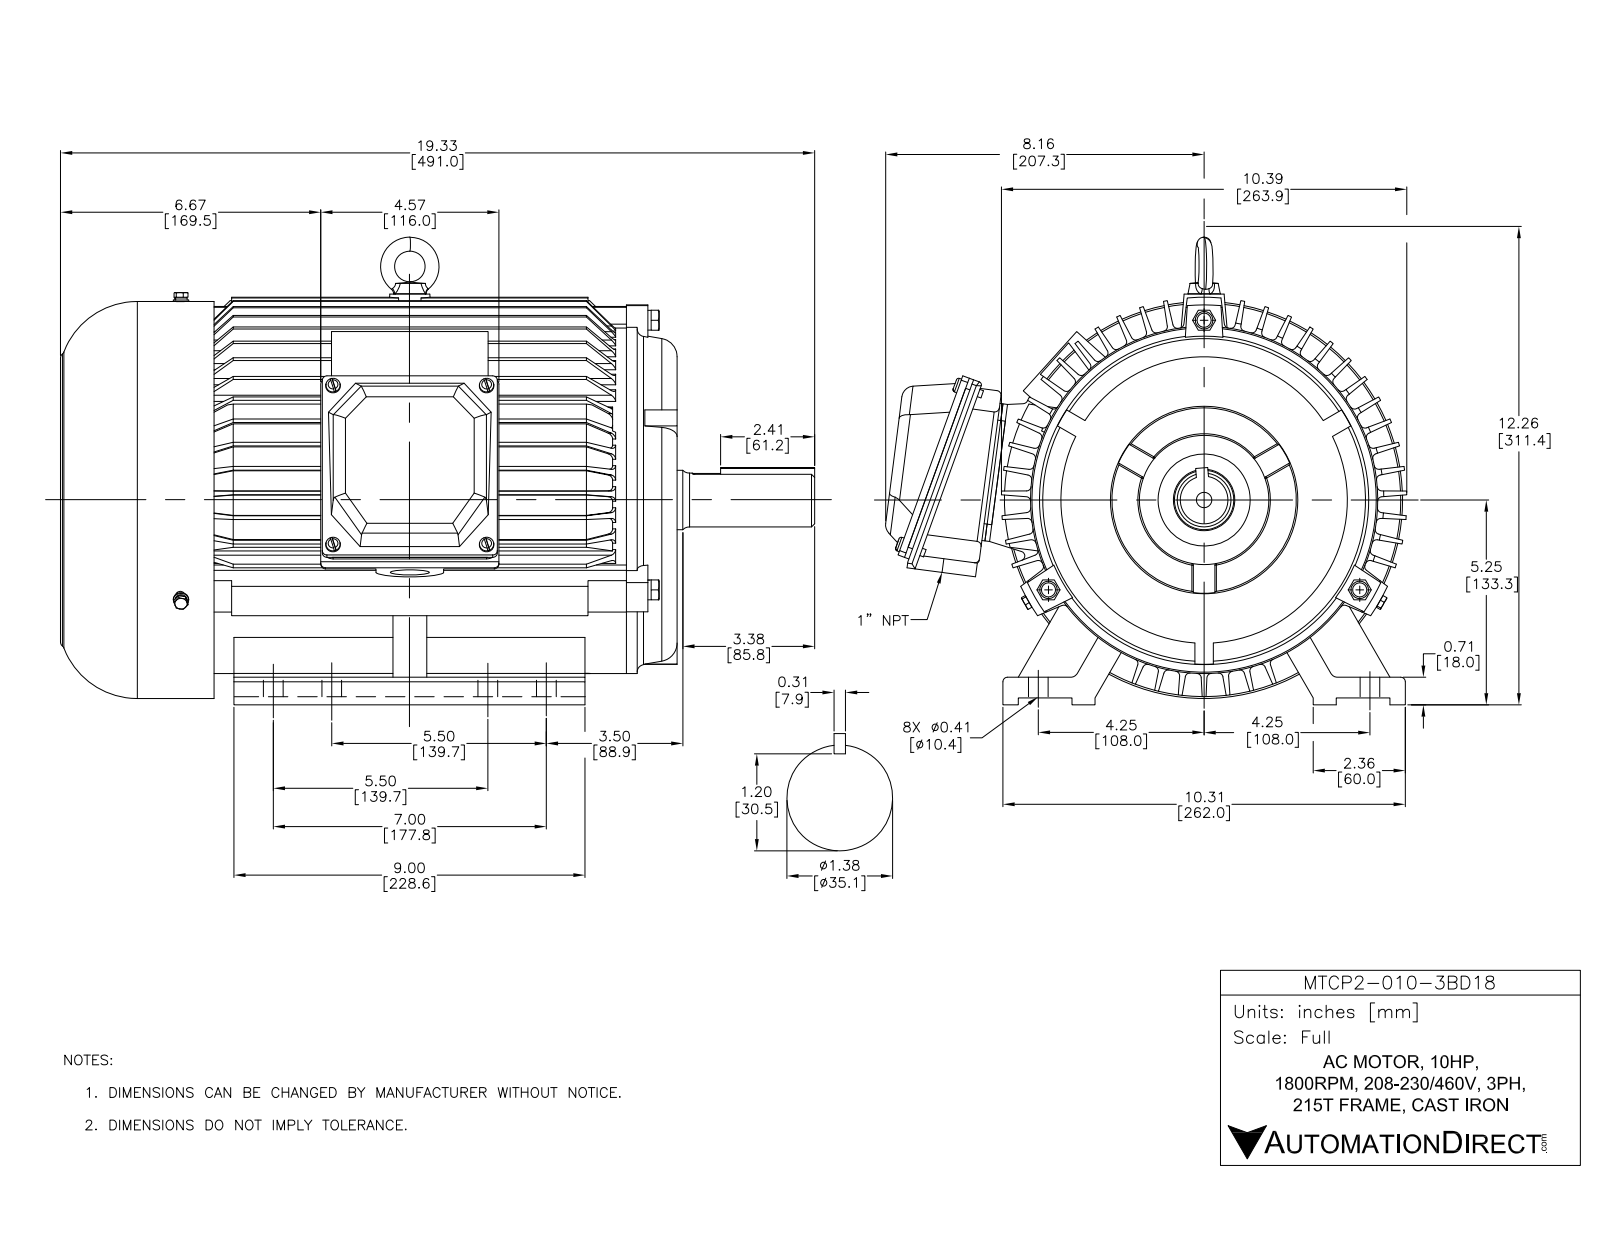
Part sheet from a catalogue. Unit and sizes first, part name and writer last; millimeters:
Units: millimetres
Overall size (bounding box): 491 × 339.3 × 304.4
Round holes (diameter × count): ⌀5.8 ×8, ⌀11 ×8, ⌀5 ×6, ⌀4.2 ×4, ⌀6 ×4, ⌀7 ×4, ⌀5.3 ×3, ⌀5.4 ×3, ⌀8 ×3, ⌀8.7 ×3, ⌀9.2 ×3, ⌀10 ×3
Round bosses / shafts (diameter × count): ⌀5 ×7, ⌀8 ×4, ⌀12.9 ×3, ⌀10 ×3, ⌀7.2 ×3, ⌀258.4 ×1, ⌀256 ×1, ⌀226 ×1
Partial cylindrical surfaces — rounded edges, fillets, slot ends (radius × count): R3 ×104, R7 ×17, R1 ×12, R1.5 ×8, R4 ×8, R8 ×8, R2.3 ×6, R11 ×6
Main face-to-face distances: 18, 4, 398.8, 1.2, 399.9, 4.5, 13.5, 6, 392.8, 394
Hole centre spacings: 100, 148.7, 110, 68, 38.1, 68, 96.1, 96.2
Volume: 4 130 000 mm³ · Surface area: 1 327 000 mm²
Bodies: 28 solids, 1831 faces (1037 planar, 523 cylindrical, 271 other)
Part name (STEP PRODUCT): PEWWE-215T
STEP written by: SolidWorks 2017 (AUTOMOTIVE_DESIGN)
